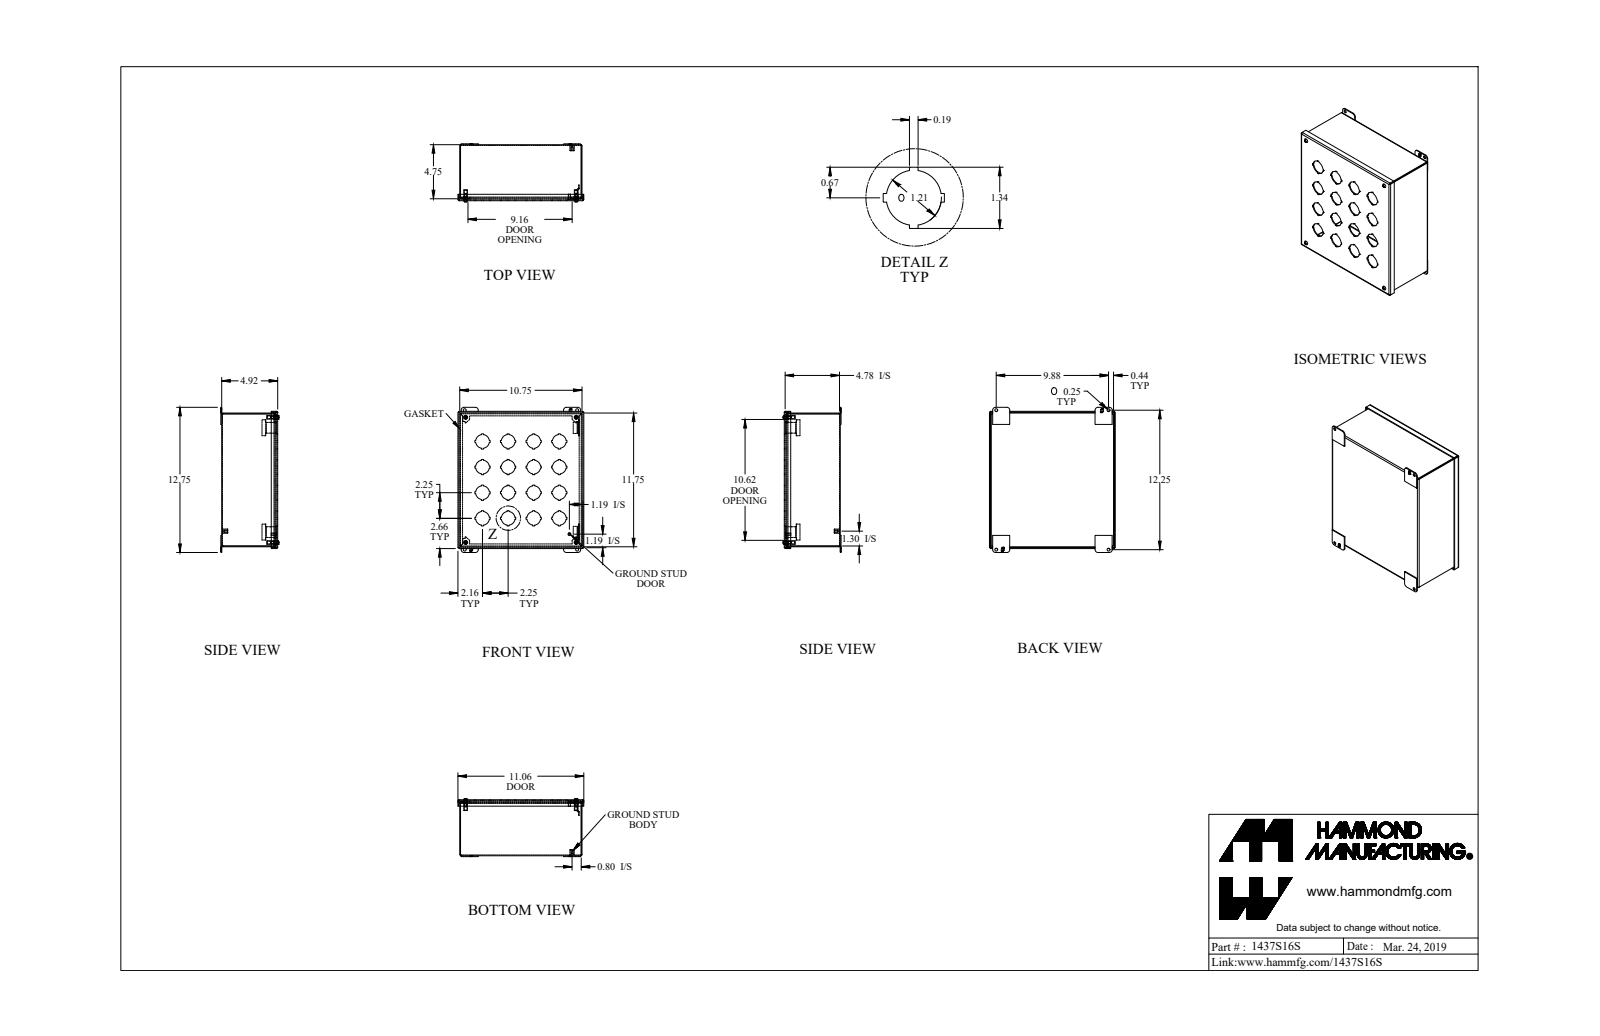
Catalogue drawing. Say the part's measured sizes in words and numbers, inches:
The part is named "1437S16S_Default". Its 3-D file was written by "SolidWorks 2019 (CONFIG_CONTROL_DESIGN)". It is 23 solids with 861 faces: 615 planar, 216 cylindrical and 30 other. Overall it measures 12.75 by 11.06 by 5.104 inches. Its volume is 39.58 cubic inches and its surface area 1 061 square inches. Round holes: 16 of diameter 1.21, 8 of diameter 0.25, 4 of diameter 0.065, 4 of diameter 0.239, 4 of diameter 0.253, 4 of diameter 0.406, 1 of diameter 0.156. Round bosses or shafts: 5 of diameter 0.19, 4 of diameter 0.406, 4 of diameter 0.315, 4 of diameter 0.148, 1 of diameter 0.375, 1 of diameter 0.25. Partial cylindrical surfaces (rounded edges, fillets, slot ends): 12 of radius 0.036, 12 of radius 0.108, 8 of radius 0.25, 4 of radius 0.029, 4 of radius 0.086, 4 of radius 0.171. The main face-to-face distances are 0.072, 4.85, 4.778, 4.922, 10.678, 0.072, 11.678, 10.606, 10.75, 11.75. The hole center spacings are 2.25, 5.031, 3.182, 4.5, 9.71, 9.711, 9.813, 10.999.
